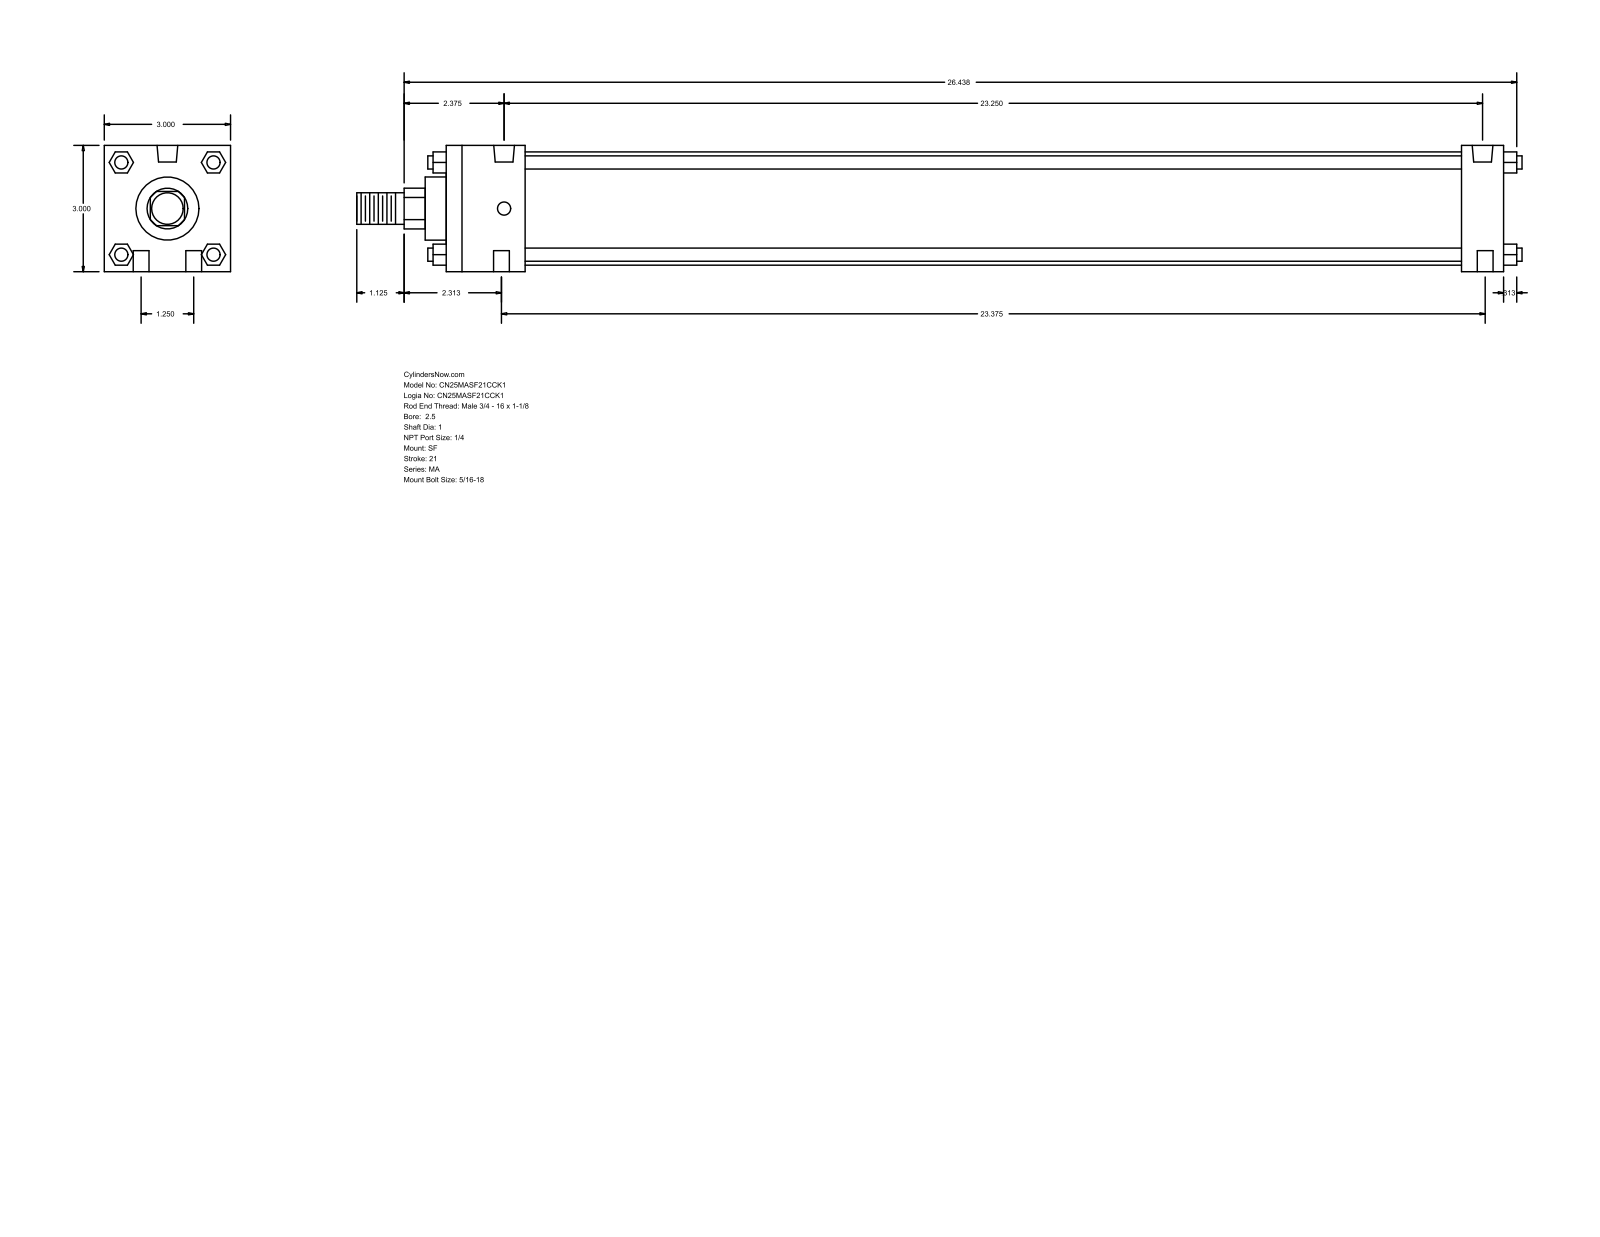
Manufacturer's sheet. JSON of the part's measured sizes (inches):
{"part_name": "MA_SF__0250_1", "step_written_by": "GSSL Pune (CONFIG_CONTROL_DESIGN)", "units": "inches", "bodies": {"solids": 0, "faces": 124, "planar": 94, "cylindrical": 30, "other": 0}, "overall_size": [27.687, 3, 3], "round_holes": [[0.375, 4], [0.313, 2], [0.492, 2]], "round_bosses_or_shafts": [[0.313, 4], [2.69, 1], [1.5, 1], [1, 1], [0.75, 1]], "partial_cylinders_radius": [[0.484, 1]], "face_to_face_distances": [3, 25.125, 0.5, 24.125, 1, 1.875, 22.25, 23.25, 1.095, 1.896], "hole_center_spacings": [0.628, 1.25, 23.25, 23.32, 23.321, 23.375, 23.408]}
